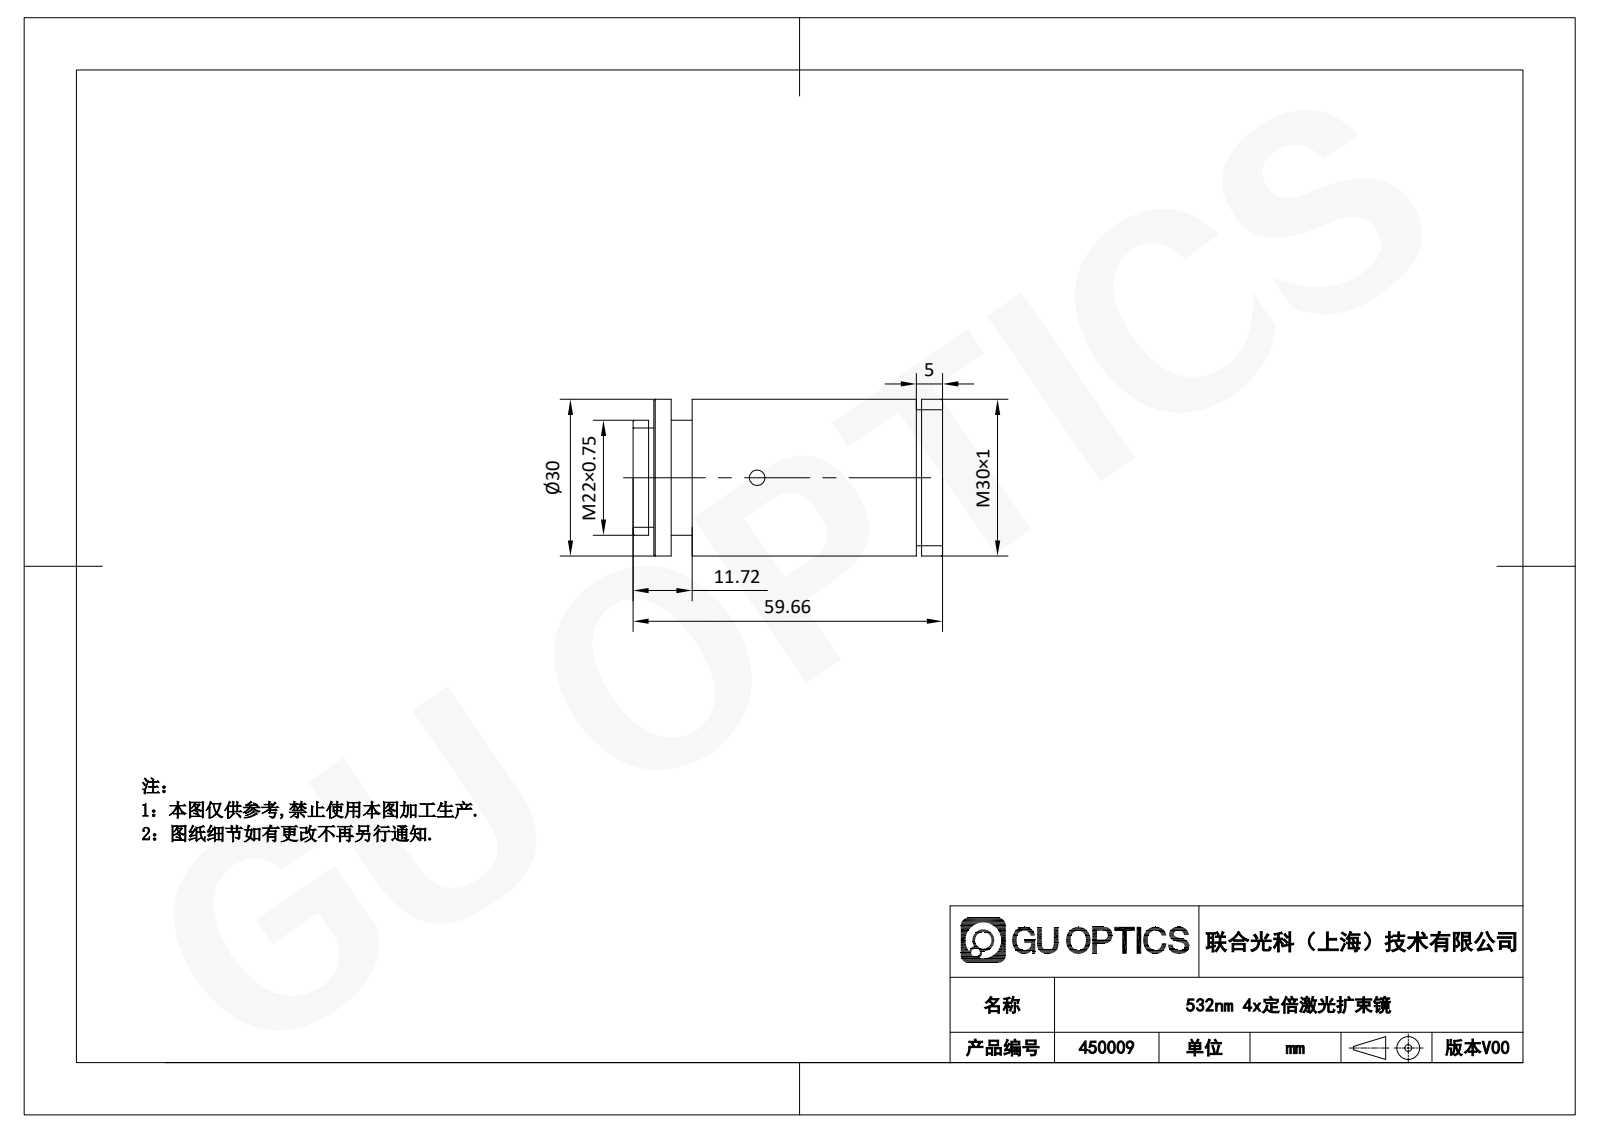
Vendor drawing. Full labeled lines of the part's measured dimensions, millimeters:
Part name (STEP PRODUCT): 450009
STEP written by: SolidWorks 2020 (AUTOMOTIVE_DESIGN)
Units: millimetres
Bodies: 1 solid, 43 faces (11 planar, 22 cylindrical, 10 other)
Overall size (bounding box): 59.66 × 30 × 30
Volume: 32 055 mm³ · Surface area: 10 637 mm²
Round holes (diameter × count): ⌀8 ×1, ⌀18 ×1
Round bosses / shafts (diameter × count): ⌀30 ×1, ⌀26 ×1, ⌀22 ×1, ⌀19 ×1
Main face-to-face distances: 4, 55.66, 47.94, 7.72, 51.66, 3.72, 51.94, 43.94, 1, 11.72
